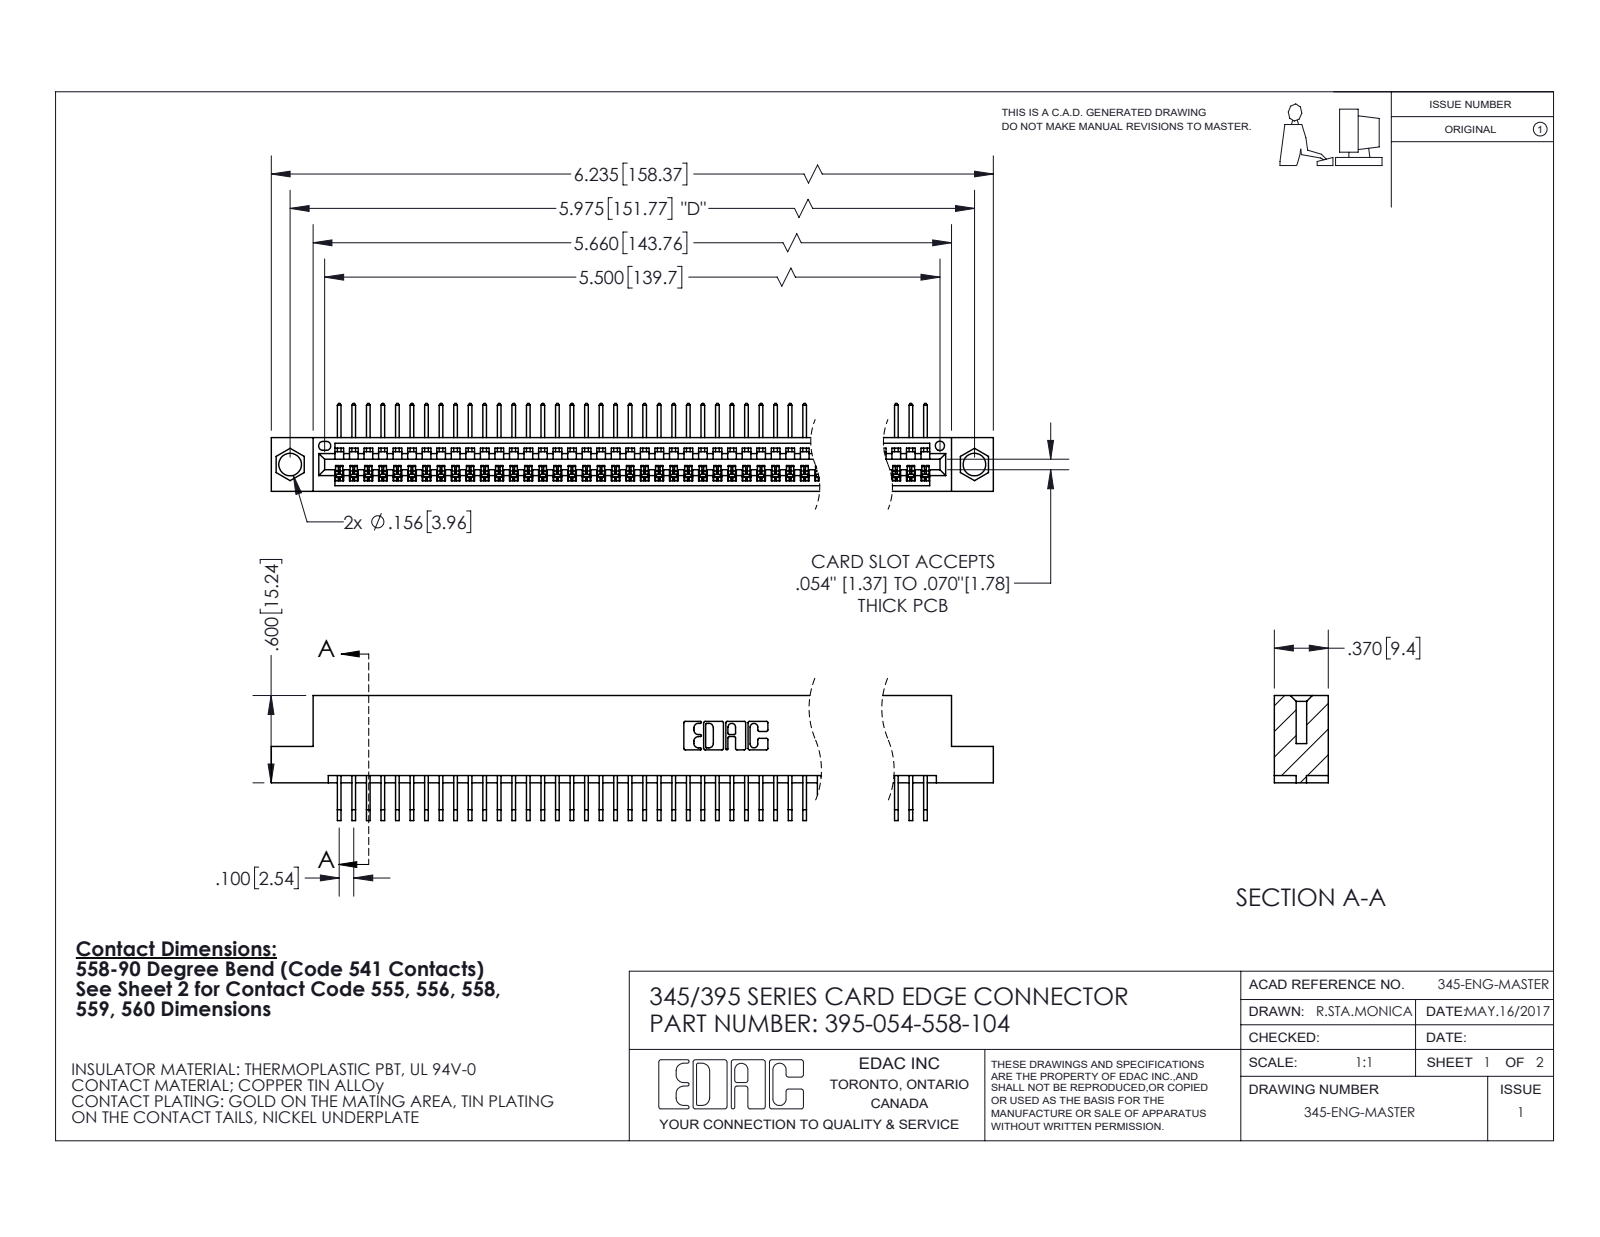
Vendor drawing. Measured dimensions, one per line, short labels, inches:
name: 345 Part_Flush Mounting Lugs - 0.156 Dia-TI; 395-054-558-104; 345-292-001_558 Tail - 2
written by: SolidWorks 2020 (CONFIG_CONTROL_DESIGN)
unit: in
bodies: 55 solids, 3380 faces (2362 planar, 1018 cylindrical, 0 other)
size: 6.235 × 0.859 × 0.605
volume: 0.928 in³; area: 32.99 in²
holes: 2× ⌀0.156, 1× ⌀0.064
rounds: 108× R0.006, 22× R0.01, 6× R0.007, 6× R0.031, 3× R0.026, 2× R0.031, 2× R0.04, 1× R0.014
face distances: 0.072, 0.298, 0.37, 0.2, 0.098, 0.272, 0.025, 0.225, 0.149, 0.072
hole spacings: 0.27, 5.739, 5.975
